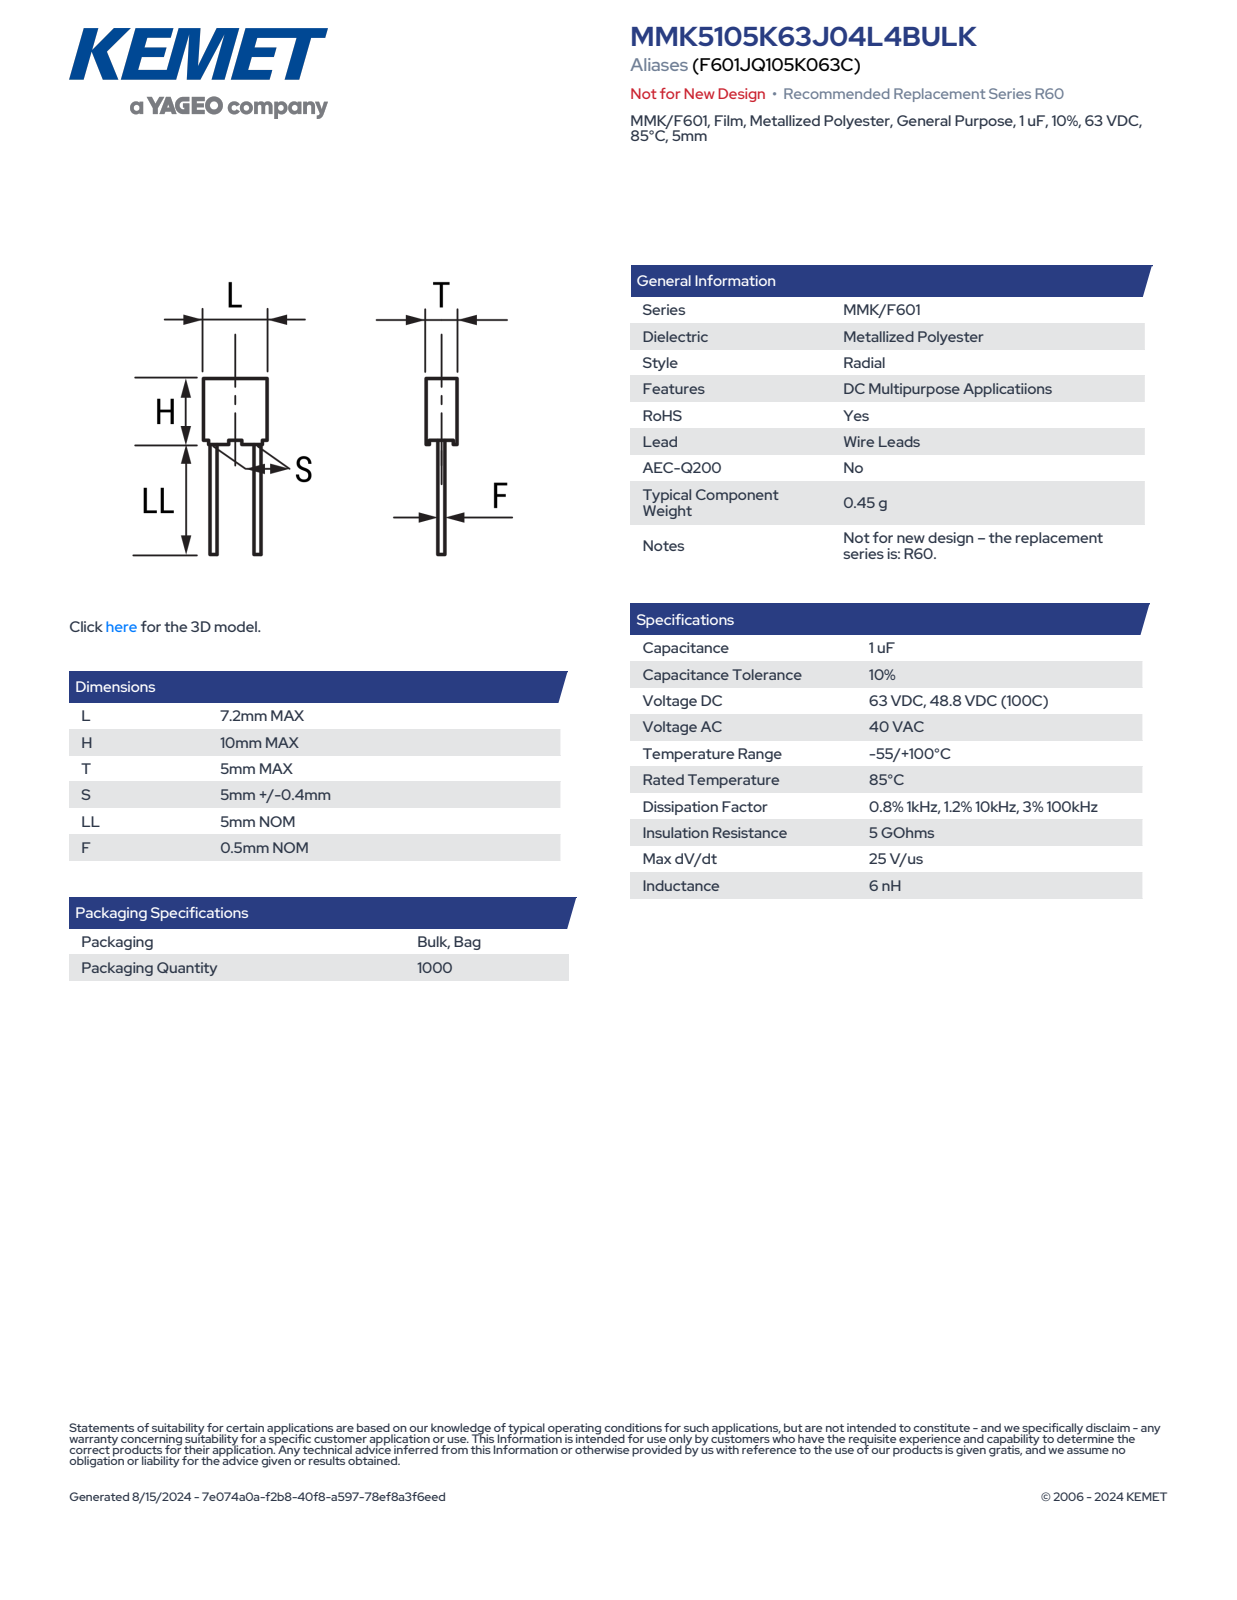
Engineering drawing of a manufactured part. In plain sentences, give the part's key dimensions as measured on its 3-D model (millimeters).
The part is named "CFR_RB3_7.2X10X5_L7.2H10T5S5LL5F0.5". Its 3-D file was written by "SolidWorks 2014 (AUTOMOTIVE_DESIGN)". It is 4 solids with 85 faces: 77 planar, 8 cylindrical and 0 other. Overall it measures 15 by 7.2 by 5 millimeters. Its volume is 338 cubic millimeters and its surface area 347 square millimeters. Round bosses or shafts: 2 of diameter 0.5. Partial cylindrical surfaces (rounded edges, fillets, slot ends): 4 of radius 0.5. The main face-to-face distances are 5, 7.2, 9.25, 4.76, 6.96, 0.75, 10, 4.52, 6.72, 9.66.
